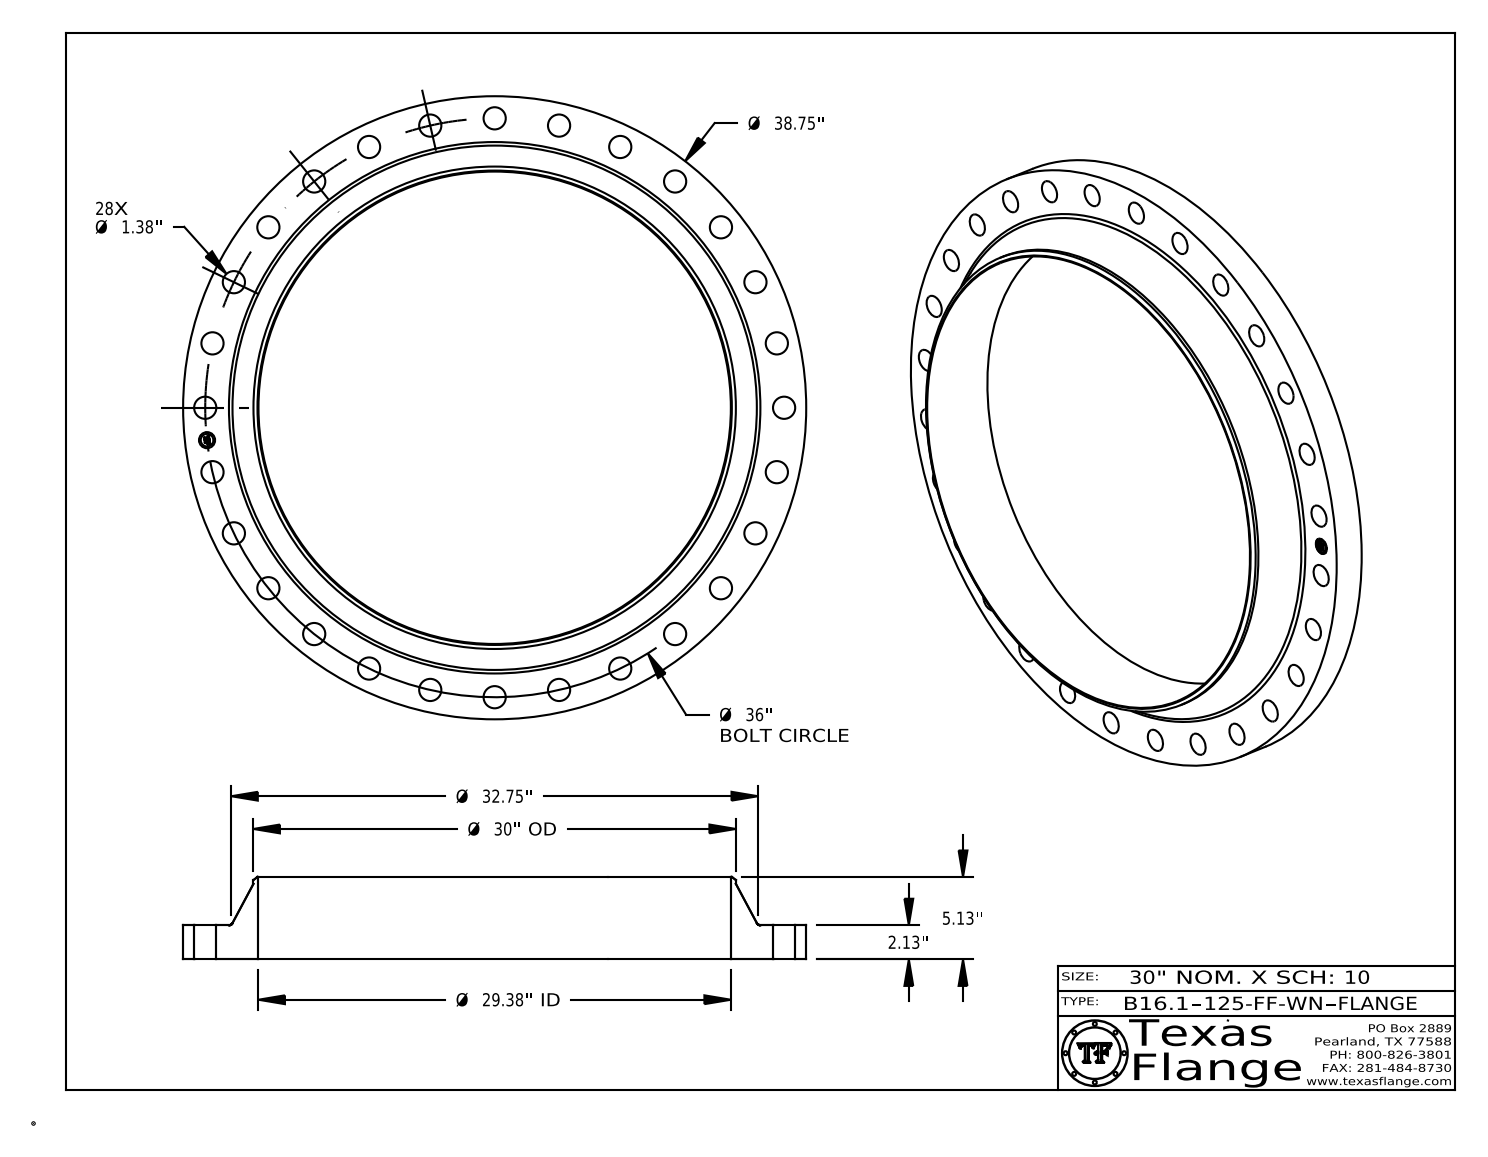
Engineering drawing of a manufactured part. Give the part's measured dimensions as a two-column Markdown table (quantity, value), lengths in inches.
| quantity | value |
| --- | --- |
| part name | B16.1, Class 125-FF-WN |
| STEP written by | CATIA V5 STEP AP214 (AUTOMOTIVE_DESIGN) |
| units | inches |
| bodies | 1 solid, 456 faces (368 planar, 82 cylindrical, 6 other) |
| overall size | 38.75 × 38.75 × 5.13 |
| volume | 1 236 in³ |
| surface area | 2 088 in² |
| round holes (diameter × count) | 1.38 × 28, 1 × 1, 29.376 × 1 |
| round bosses / shafts (diameter × count) | 0.061 × 8, 38.75 × 1, 30 × 1, 0.788 × 1 |
| main face-to-face distances | 2.13, 5.13, 3, 0.015, 2.115, 3.015, 0.298, 0.293, 0.054, 0.193 |
| hole center spacings | 18, 19.153, 4.031, 8.011, 11.89, 15.62, 22.446, 25.456 |
